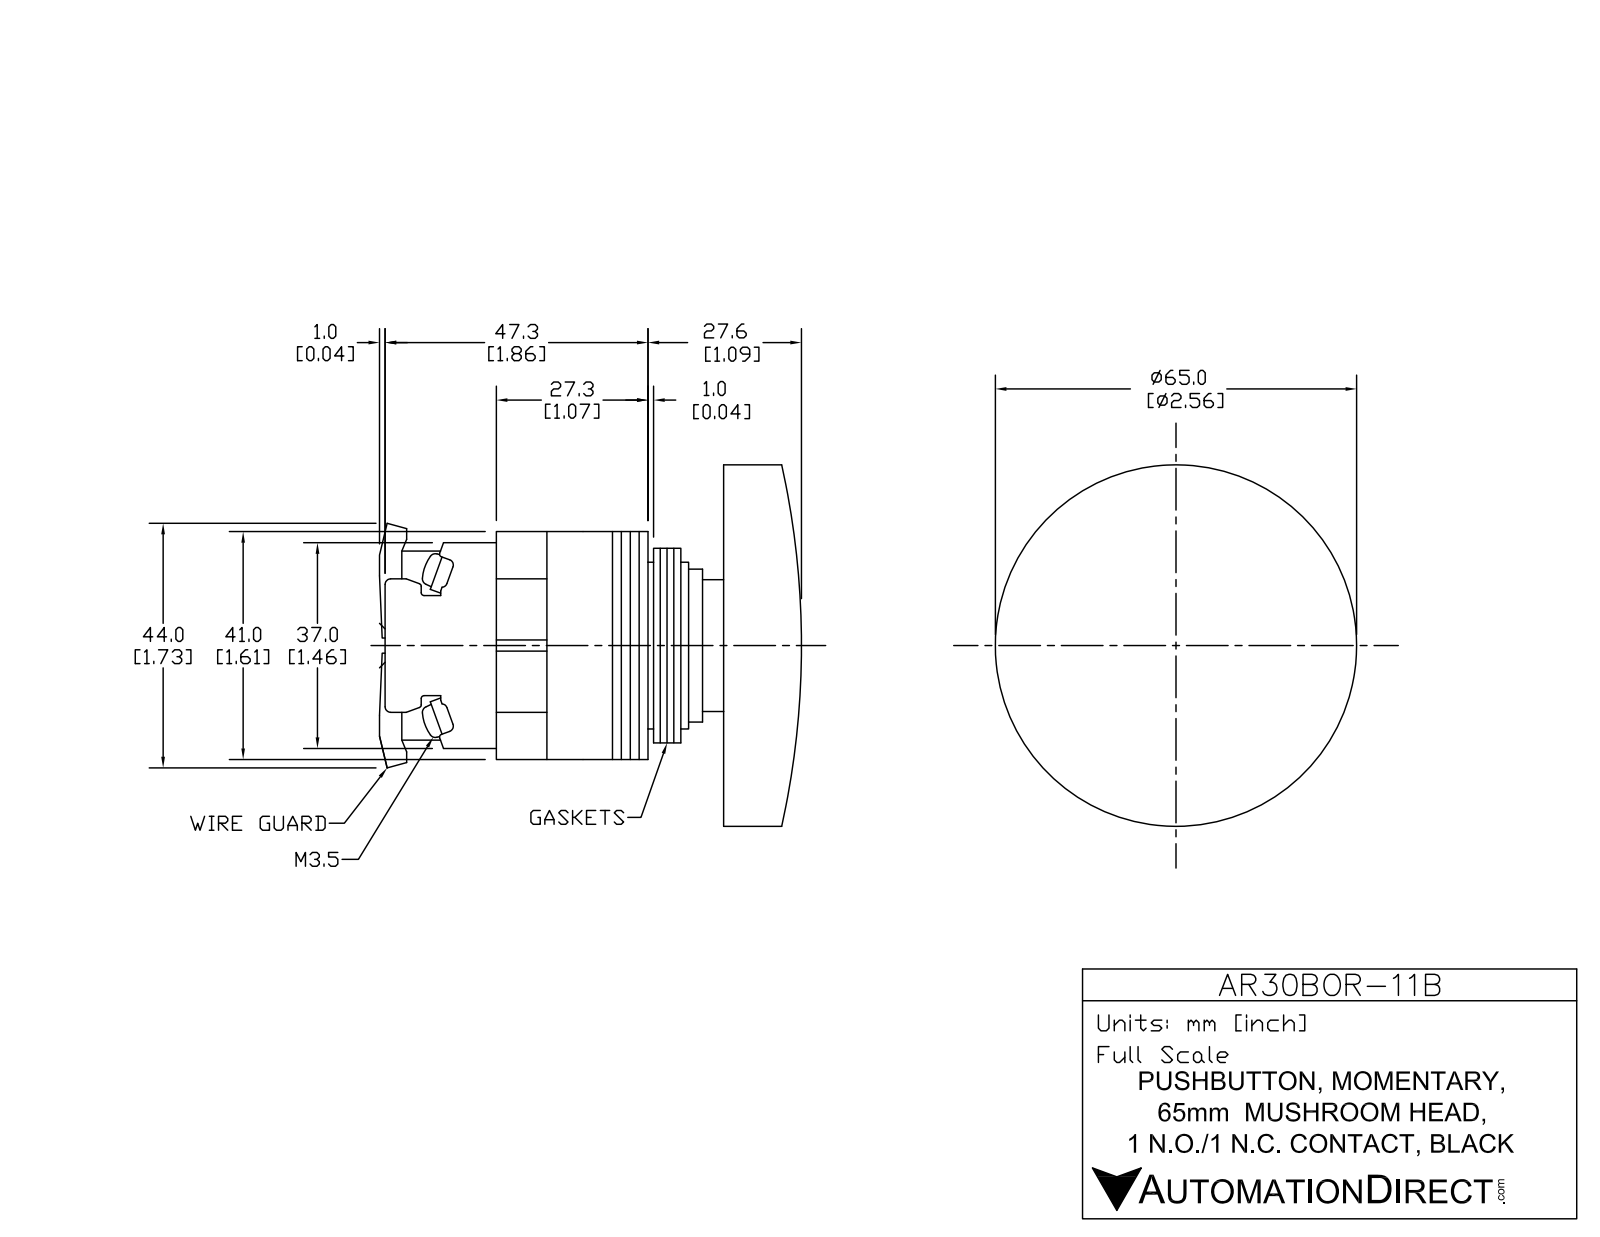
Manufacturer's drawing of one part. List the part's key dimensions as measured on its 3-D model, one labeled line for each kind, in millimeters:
Part name (STEP PRODUCT): AR30B0R-11B
STEP written by: SolidWorks 2017 (AUTOMOTIVE_DESIGN)
Units: millimetres
Bodies: 20 solids, 381 faces (236 planar, 127 cylindrical, 18 other)
Overall size (bounding box): 76 × 65 × 65
Volume: 83 080 mm³ · Surface area: 42 286 mm²
Round holes (diameter × count): ⌀3 ×4, ⌀24 ×1, ⌀30 ×1, ⌀60 ×1
Round bosses / shafts (diameter × count): ⌀5 ×4, ⌀65 ×1, ⌀40 ×1, ⌀35 ×1, ⌀29.8 ×1
Partial cylindrical surfaces — rounded edges, fillets, slot ends (radius × count): R0.5 ×16, R5 ×10, R1.75 ×8, R2 ×4, R3 ×4
Main face-to-face distances: 1.6, 21, 16, 3.2, 41, 5, 1, 4.8, 36, 15.99
Hole centre spacings: 21.92, 31, 43.84
